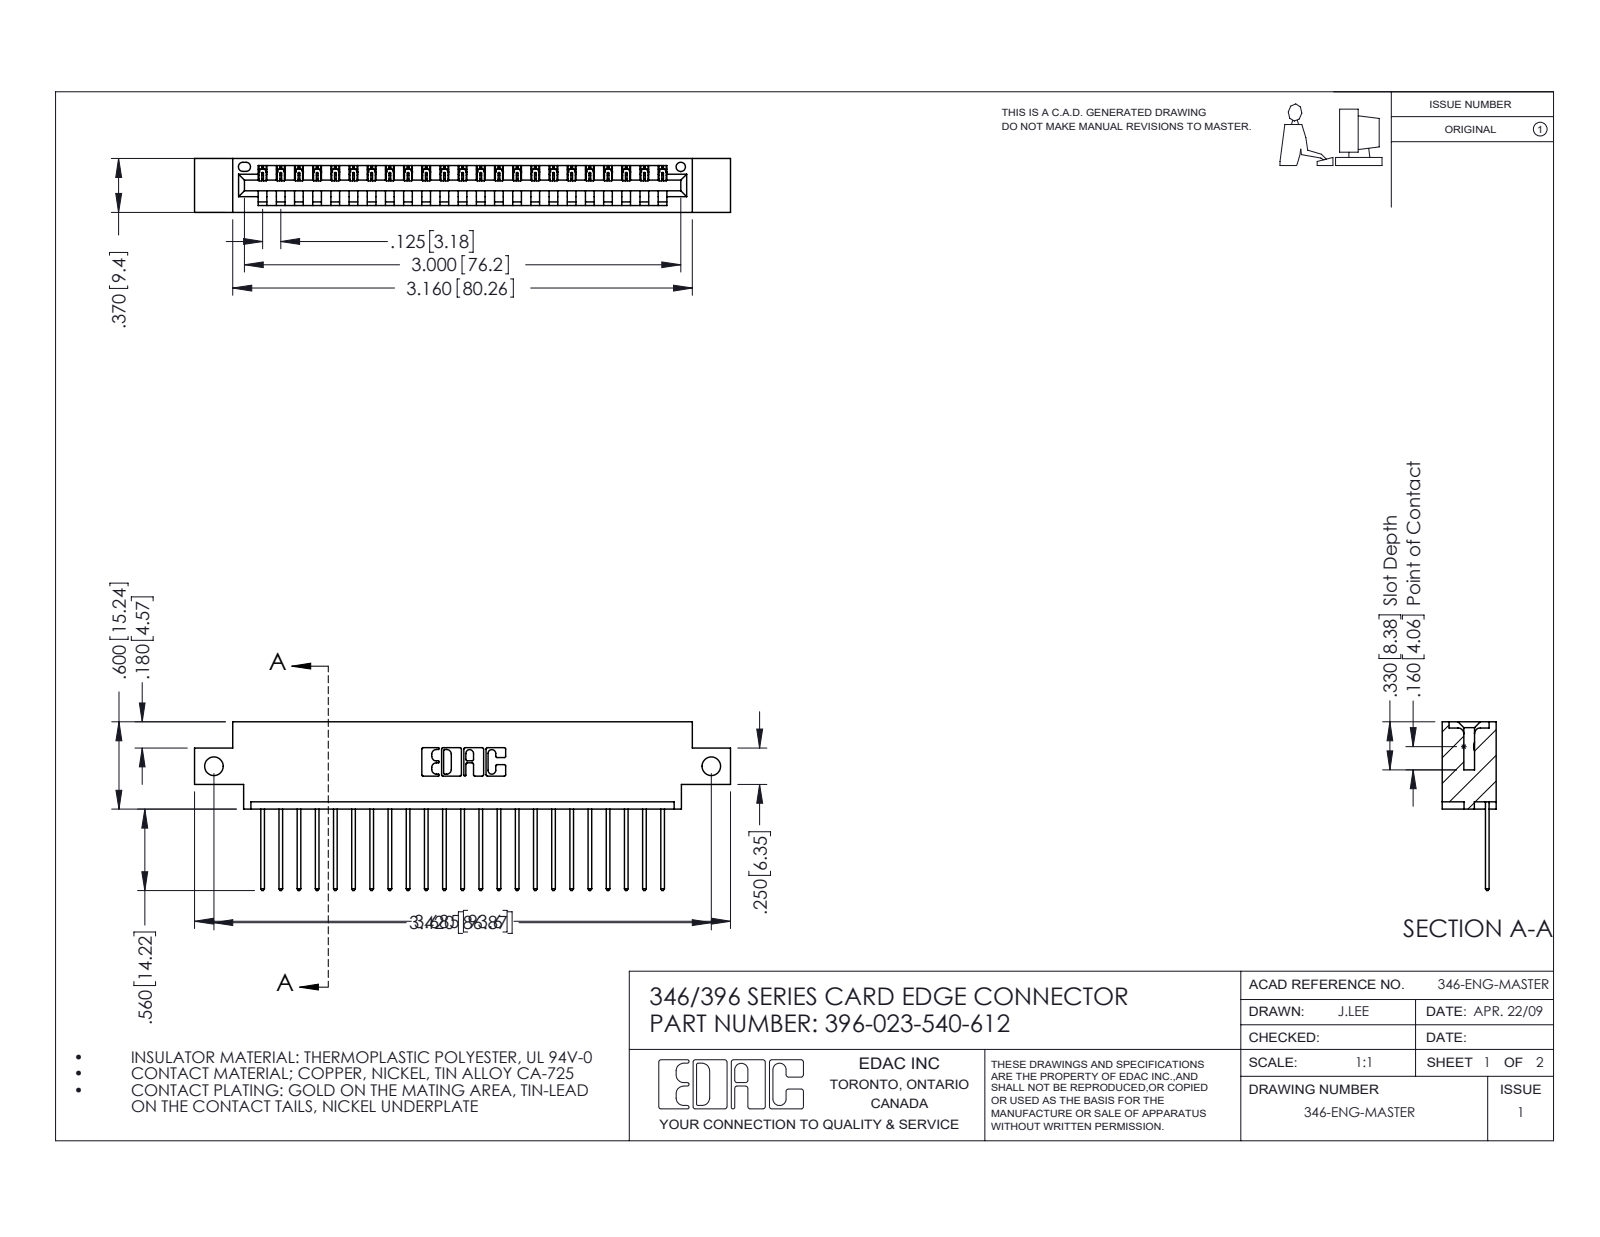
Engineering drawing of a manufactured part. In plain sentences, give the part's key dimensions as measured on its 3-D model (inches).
The part is named "345-292-001_345-293-140; 346 Part_0.170 Offset - Side Mount; 396-023-540-612". Its 3-D file was written by "SolidWorks 2016 (CONFIG_CONTROL_DESIGN)". It is 24 solids with 1460 faces: 1000 planar, 460 cylindrical and 0 other. Overall it measures 3.685 by 1.16 by 0.37 inches. Its volume is 0.526 cubic inches and its surface area 16.75 square inches. Round holes: 2 of diameter 0.128, 1 of diameter 0.064. Partial cylindrical surfaces (rounded edges, fillets, slot ends): 46 of radius 0.006, 46 of radius 0.01, 22 of radius 0.01, 6 of radius 0.007, 6 of radius 0.031, 3 of radius 0.026, 2 of radius 0.031, 2 of radius 0.04. The main face-to-face distances are 0.048, 0.322, 0.37, 0.25, 0.072, 0.298, 0.025, 0.148, 0.222, 0.1. The hole center spacings are 3.42.
